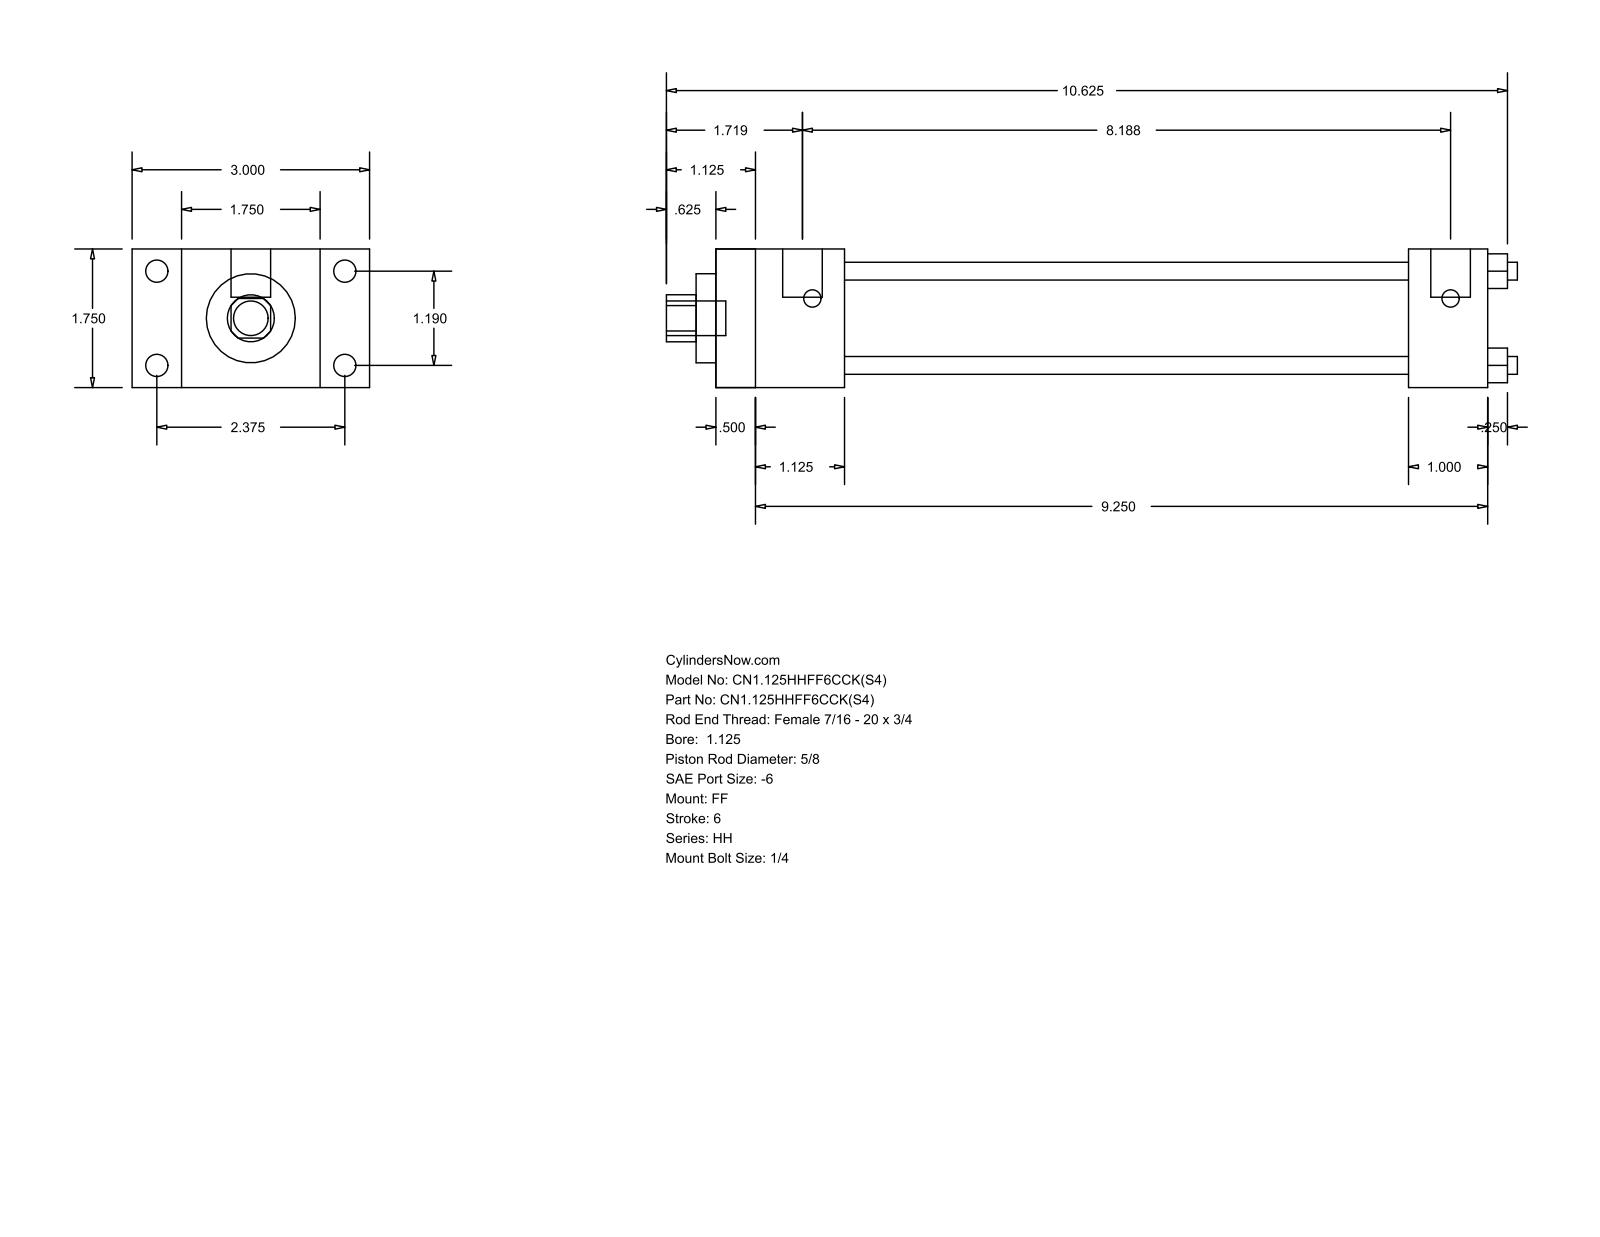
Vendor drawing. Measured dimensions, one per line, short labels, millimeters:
name: HH_FF__0112_0.625
written by: GSSL Pune (CONFIG_CONTROL_DESIGN)
unit: mm
bodies: 0 solids, 92 faces (64 planar, 28 cylindrical, 0 other)
size: 273.05 × 76.2 × 44.45
holes: 4× ⌀5.71, 1× ⌀15.88, 1× ⌀28.57, 1× ⌀34.92
bosses: 4× ⌀7.14, 4× ⌀5.56, 2× ⌀12.7, 1× ⌀11.11
rounds: 1× R7.54
face distances: 44.46, 247.64, 12.69, 234.95, 15.87, 60.33, 28.58, 41.27, 222.24, 209.55
hole spacings: 21.37, 30.22, 42.74
